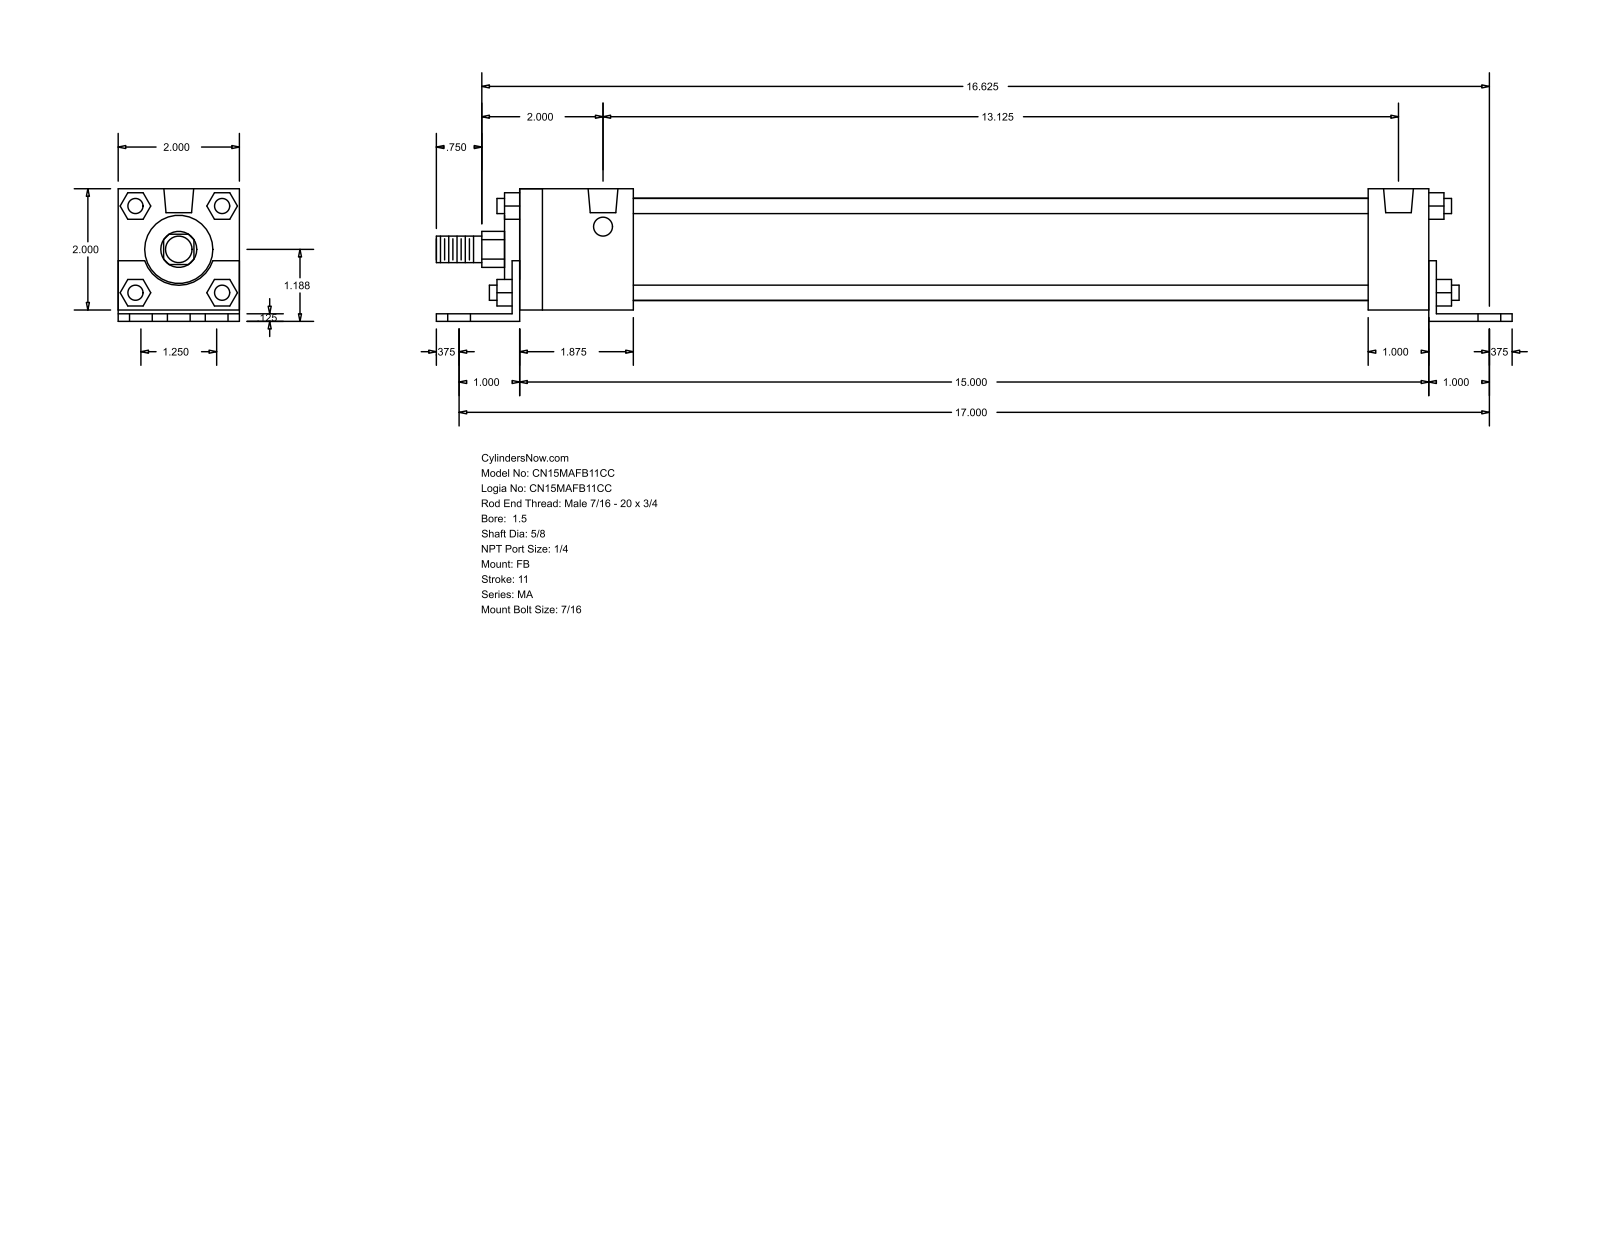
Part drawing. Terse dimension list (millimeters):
name: MA_FB__0150_0.625
written by: GSSL Pune (CONFIG_CONTROL_DESIGN)
unit: mm
bodies: 0 solids, 140 faces (105 planar, 35 cylindrical, 0 other)
size: 450.85 × 55.56 × 50.8
holes: 6× ⌀11.11, 4× ⌀7.94, 2× ⌀12.49
bosses: 4× ⌀6.35, 1× ⌀42.93, 1× ⌀28.57, 1× ⌀15.88, 1× ⌀11.11
rounds: 1× R7.54, 1× R15.05
face distances: 50.8, 3.17, 4.76, 55.56, 1.59, 52.39, 25.4, 387.35, 6.35, 3.18
hole spacings: 15.88, 432.09, 431.8, 31.76, 41.27, 62.38, 333.38, 371.81
